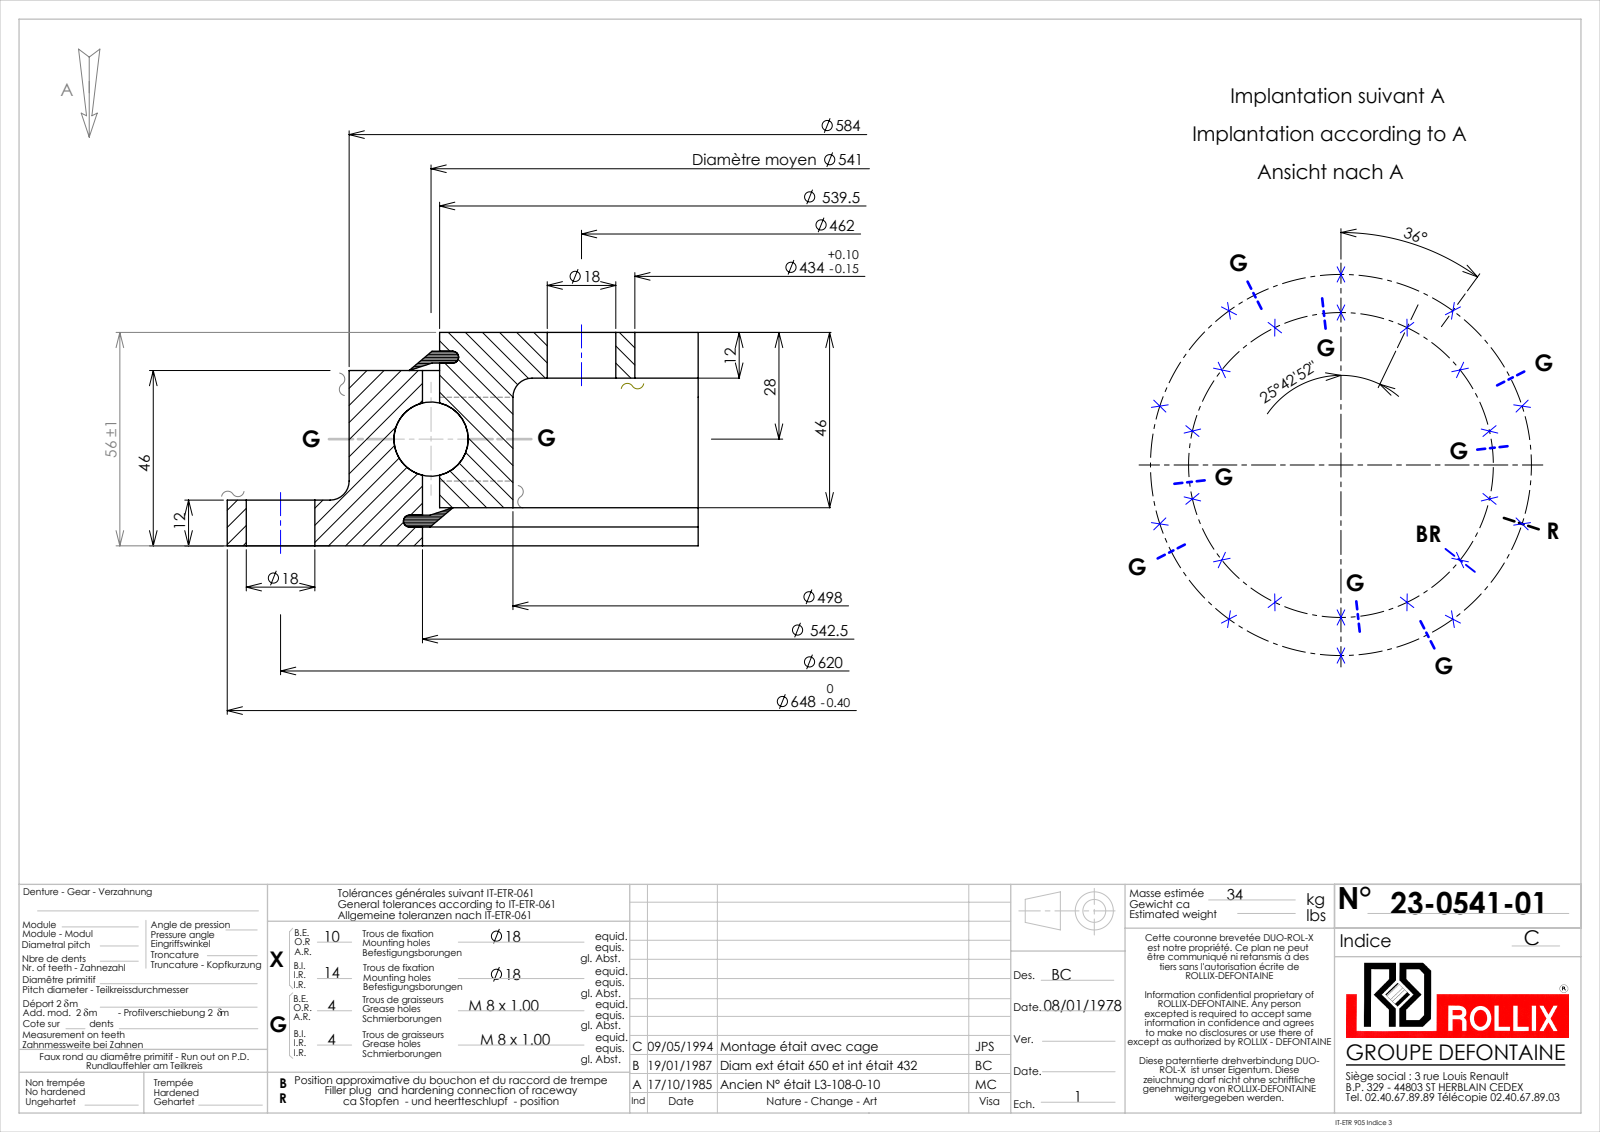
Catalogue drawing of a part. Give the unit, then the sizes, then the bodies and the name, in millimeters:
Units: millimetres
Overall size (bounding box): 648 × 648 × 56
Round holes (diameter × count): ⌀18 ×24, ⌀7 ×8, ⌀434 ×1, ⌀498 ×1, ⌀545.5 ×1
Round bosses / shafts (diameter × count): ⌀8 ×8, ⌀648 ×1, ⌀584 ×1, ⌀536.5 ×1
Main face-to-face distances: 12, 44, 56, 10, 46, 2, 34, 32, 36, 8.05
Hole centre spacings: 231, 416.25, 310, 450.42, 589.66, 102.81, 191.59, 200.45
Volume: 3 959 000 mm³ · Surface area: 819 702 mm²
Bodies: 13 solids, 306 faces (94 planar, 100 cylindrical, 112 other)
Part name (STEP PRODUCT): 23-0541-01
STEP written by: SolidWorks 2016 (CONFIG_CONTROL_DESIGN)
